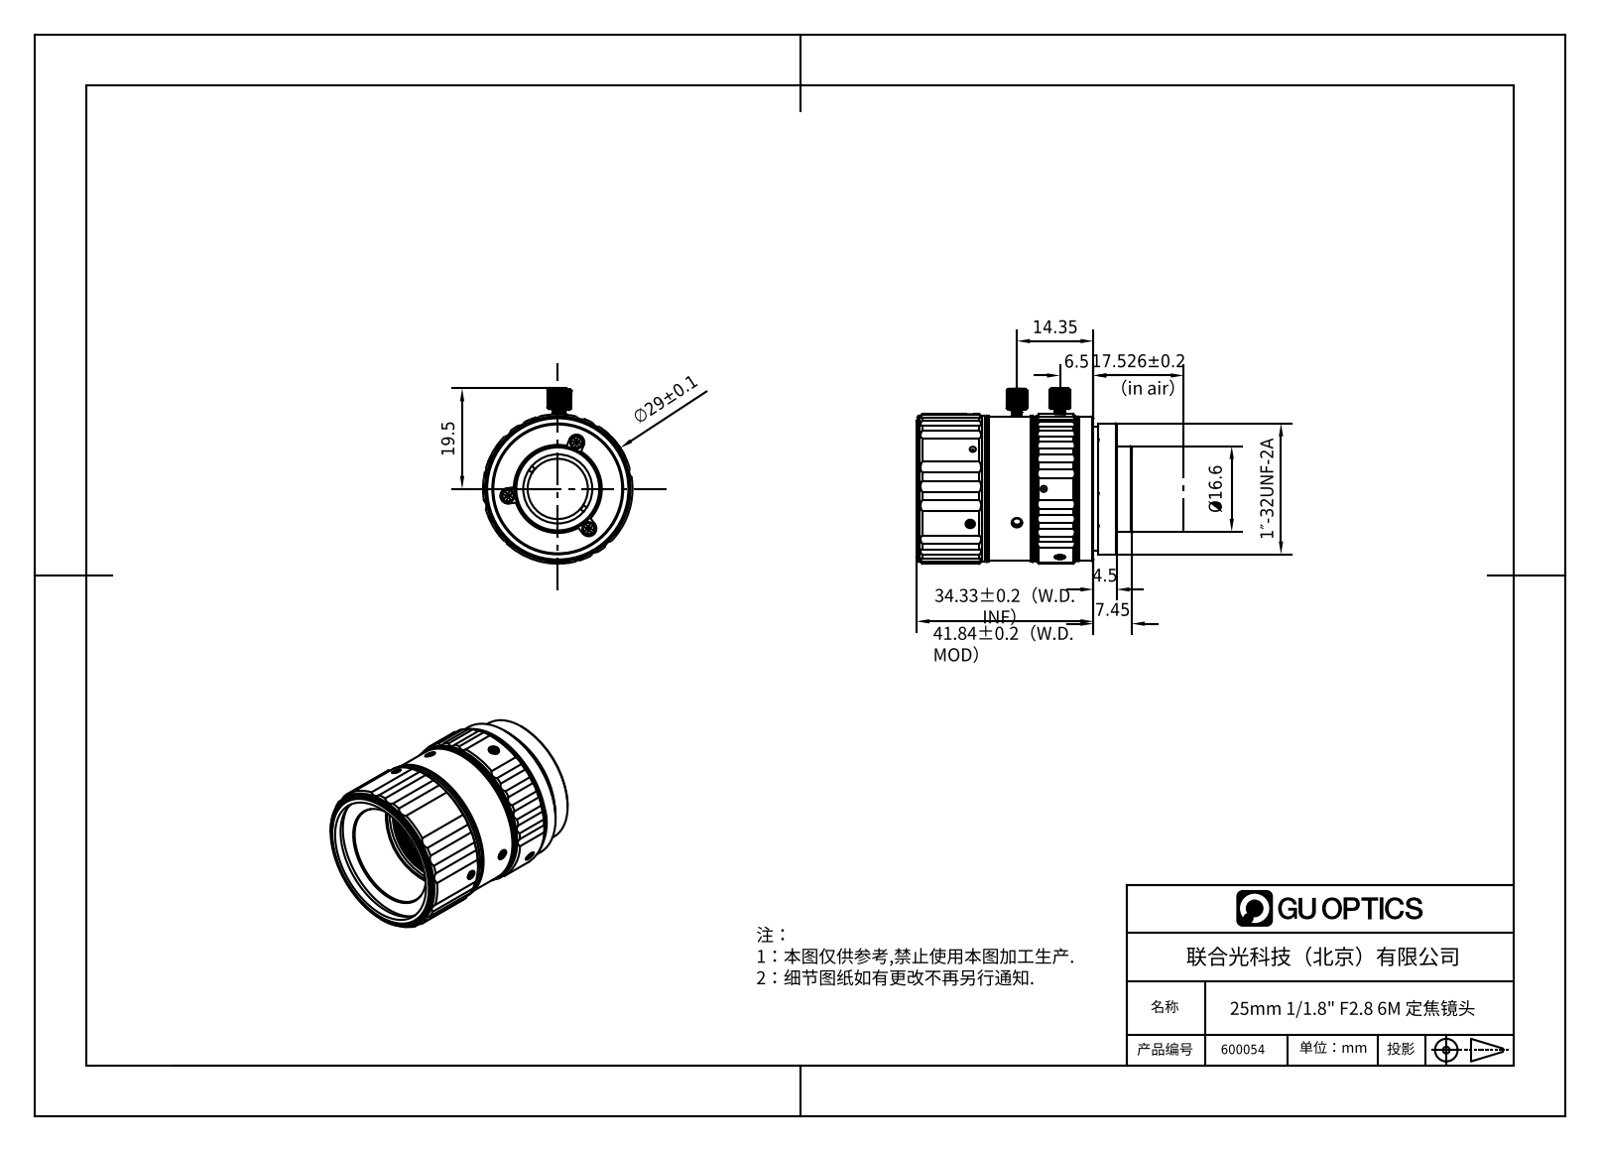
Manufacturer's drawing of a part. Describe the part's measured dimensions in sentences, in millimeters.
The part is named "600054". Its 3-D file was written by "SolidWorks 2020 (CONFIG_CONTROL_DESIGN)". It is 10 solids with 1167 faces: 293 planar, 588 cylindrical and 286 other. Overall it measures 41.78 by 31.37 by 29 millimeters. Its volume is 19 561 cubic millimeters and its surface area 8 897 square millimeters. Round holes: 6 of diameter 1.22, 6 of diameter 1.65, 6 of diameter 2, 3 of diameter 1.7, 3 of diameter 2.03, 1 of diameter 1.62, 1 of diameter 11.7, 1 of diameter 13.4, 1 of diameter 13.7, 1 of diameter 13.9, 1 of diameter 14.9, 1 of diameter 16.34. Round bosses or shafts: 8 of diameter 1.6, 3 of diameter 2.5, 3 of diameter 1.2, 2 of diameter 2, 1 of diameter 29, 1 of diameter 28.4, 1 of diameter 28.2, 1 of diameter 28. Partial cylindrical surfaces (rounded edges, fillets, slot ends): 25 of radius 1.5, 18 of radius 2.3, 6 of radius 1.11, 6 of radius 3.39, 6 of radius 3.43, 2 of radius 0.6, 2 of radius 1.12, 2 of radius 2. The main face-to-face distances are 36.34, 4.5, 31.84, 2, 24.87, 20.37, 11.47, 1, 32.84, 23.37. The hole center spacings are 9.05, 16.89, 9.75, 9.74.
